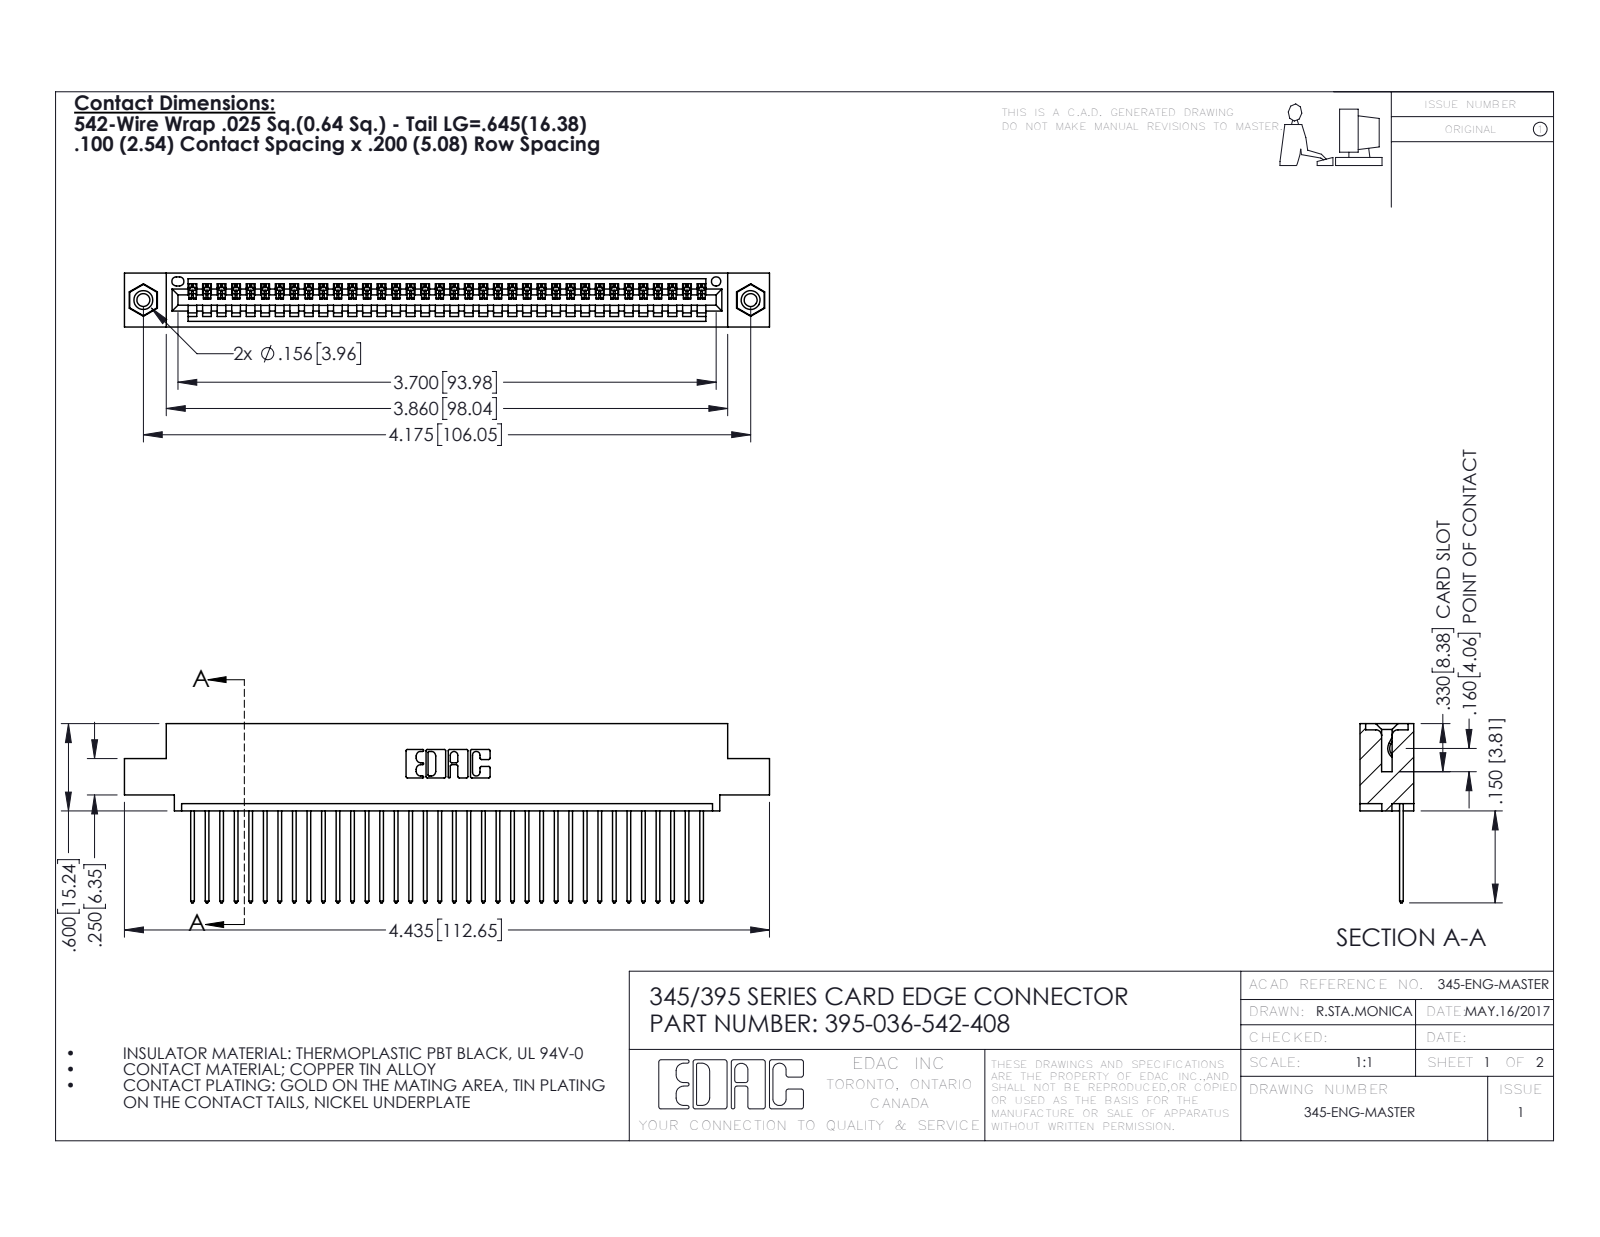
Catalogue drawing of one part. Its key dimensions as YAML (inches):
part_name: "345-292-001_345-293-142; 345-250-001_345-250-003-102; 345 Part_0.110 Offset - 0.156 Dia-TI; 395-036-542-408"
step_written_by: "SolidWorks 2016 (CONFIG_CONTROL_DESIGN)"
units: inches
bodies: {solids: 39, faces: 2278, planar: 1556, cylindrical: 706, other: 16}
overall_size: [4.435, 1.232, 0.37]
volume: 0.65
surface_area: 22.75
round_holes:
  - {diameter: 0.089, count: 2}
  - {diameter: 0.125, count: 2}
  - {diameter: 0.156, count: 2}
  - {diameter: 0.064, count: 1}
round_bosses_or_shafts:
  - {diameter: 0.155, count: 2}
partial_cylinders:
  - {radius: 0.006, count: 72}
  - {radius: 0.01, count: 72}
  - {radius: 0.01, count: 22}
  - {radius: 0.007, count: 6}
  - {radius: 0.031, count: 6}
  - {radius: 0.026, count: 3}
  - {radius: 0.031, count: 2}
  - {radius: 0.04, count: 2}
face_to_face_distances: [0.072, 0.298, 0.37, 0.098, 0.272, 0.025, 0.2, 0.225, 0.149, 0.072]
hole_center_spacings: [0.27, 3.939, 4.175]
